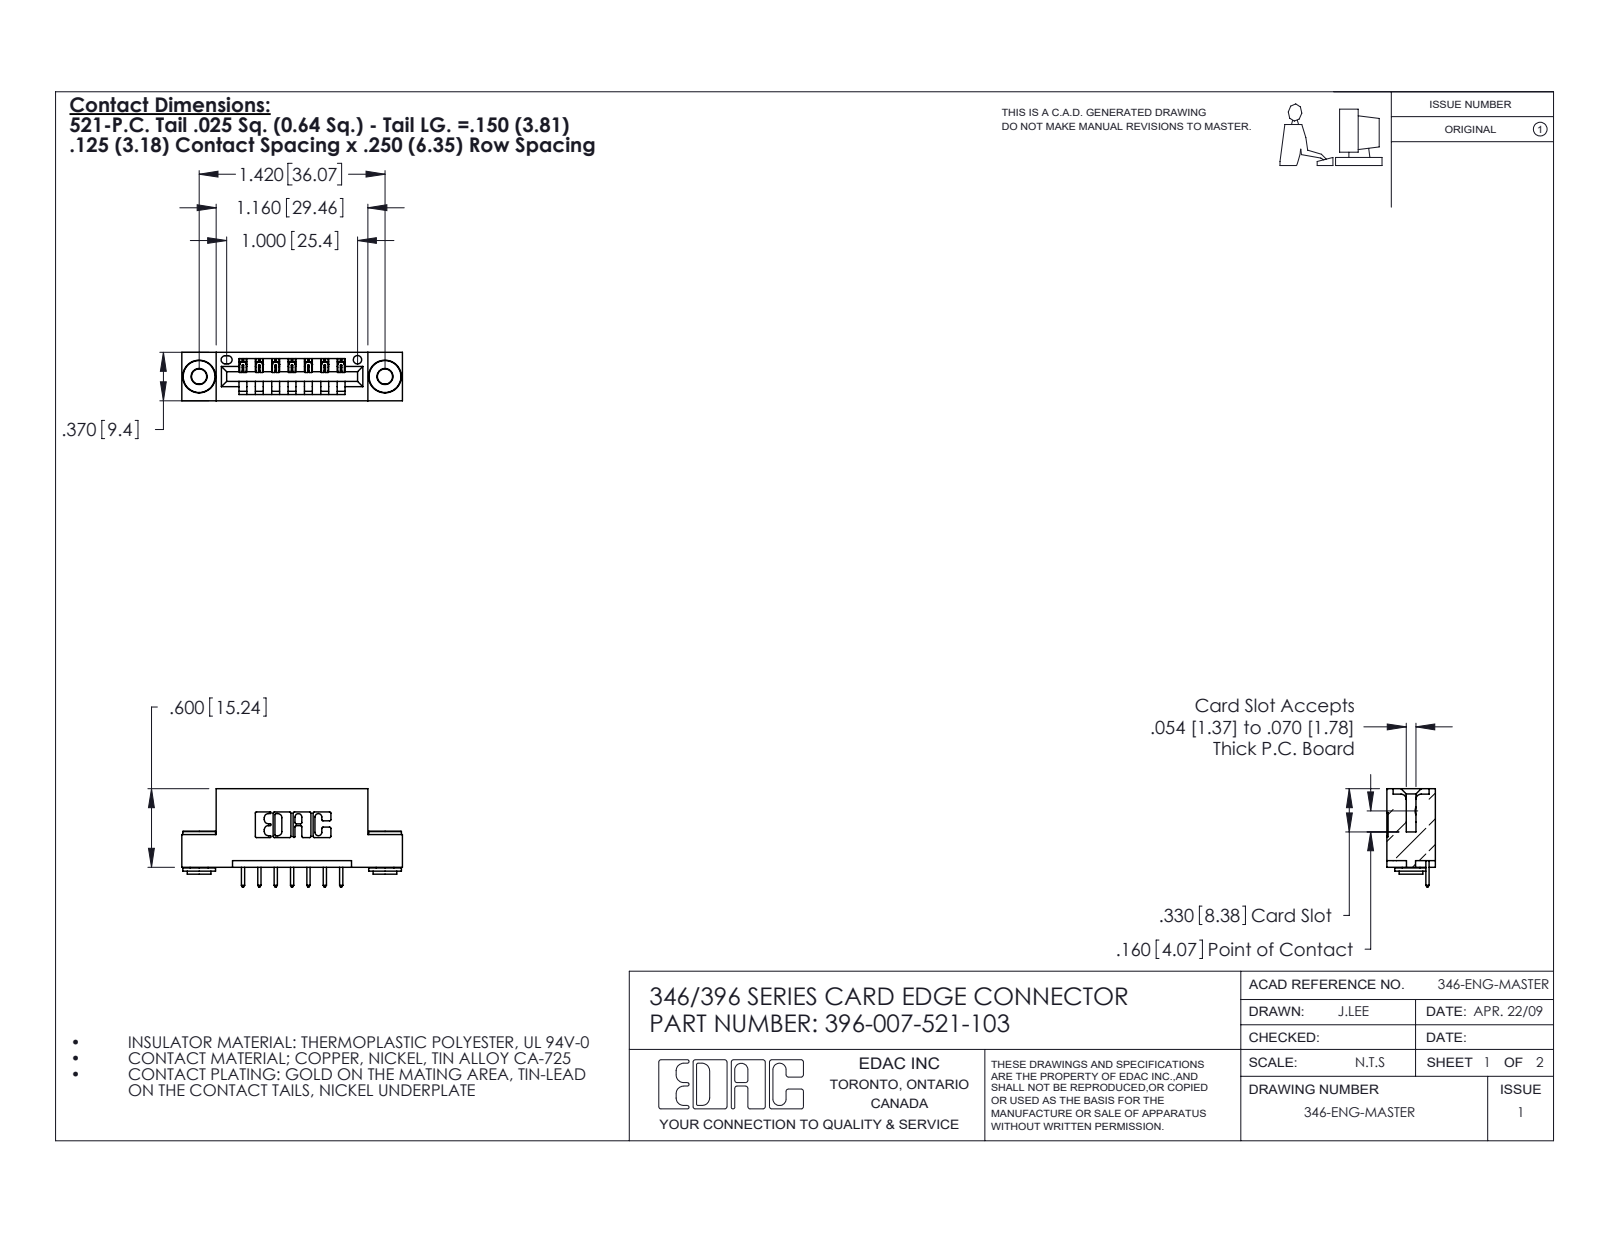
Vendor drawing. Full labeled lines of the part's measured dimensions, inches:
Part name (STEP PRODUCT): 345-250-002_345-250-002-102; 345-292-001_345-293-121; 396-007-521-103; 346 Part_Flush Mounting Lugs - 0.156 Dia-TH
STEP written by: SolidWorks 2020 (CONFIG_CONTROL_DESIGN)
Units: inches
Bodies: 10 solids, 580 faces (380 planar, 192 cylindrical, 8 other)
Overall size (bounding box): 1.685 × 0.75 × 0.37
Volume: 0.234 in³ · Surface area: 7.115 in²
Round holes (diameter × count): ⌀0.116 ×2, ⌀0.156 ×2, ⌀0.064 ×1
Round bosses / shafts (diameter × count): ⌀0.25 ×2, ⌀0.18 ×2, ⌀0.136 ×2
Partial cylindrical surfaces — rounded edges, fillets, slot ends (radius × count): R0.01 ×22, R0.006 ×14, R0.01 ×14, R0.007 ×6, R0.031 ×6, R0.026 ×3, R0.031 ×2, R0.04 ×2
Main face-to-face distances: 0.25, 0.37, 0.048, 0.322, 0.025, 0.148, 0.222, 0.1, 0.174, 0.125
Hole centre spacings: 0.246, 1.217, 1.42
